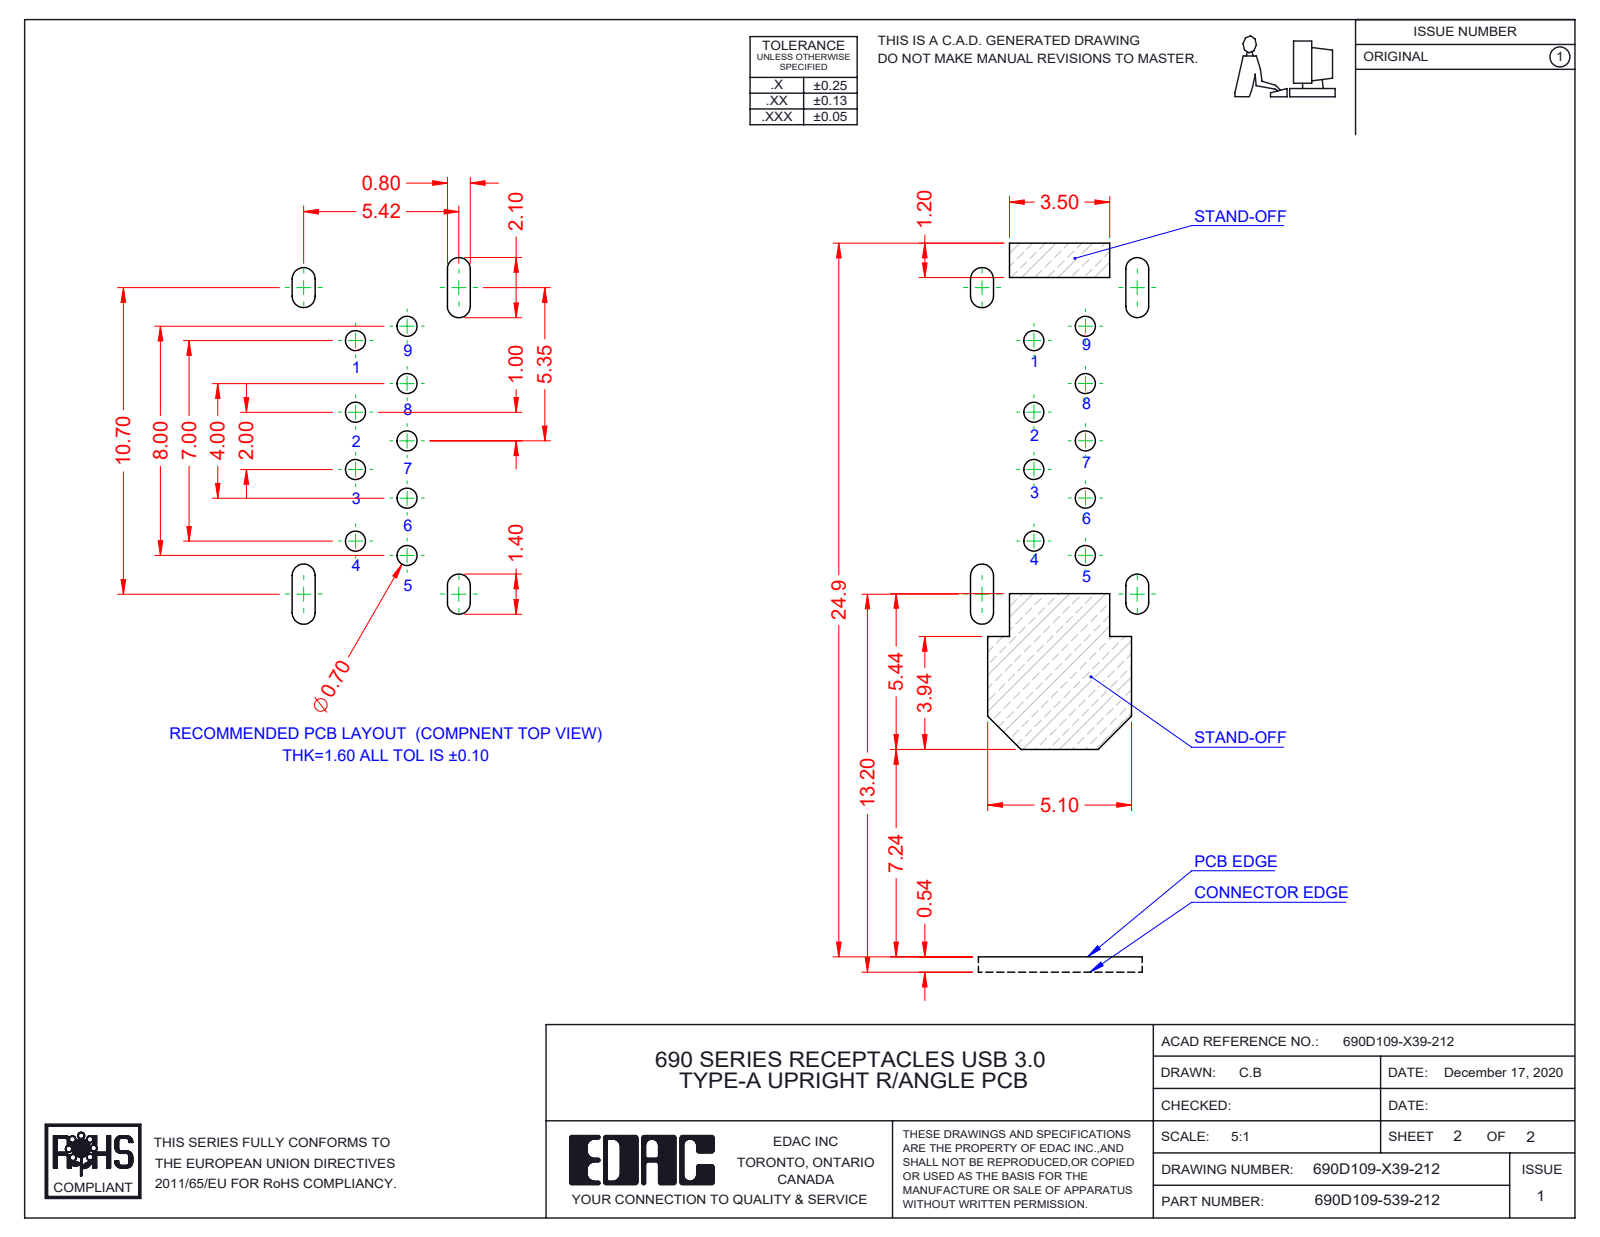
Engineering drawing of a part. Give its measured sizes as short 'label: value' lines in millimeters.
name: Contact 2.0 4 690D109-X39-212; Insulator 2 690D109-X39-212_Blue; Shell 2 690D109-X39-212; Contact 3.0 7 690D109-X39-212 (+8 more)
written by: SolidWorks 2020 (AUTOMOTIVE_DESIGN)
unit: mm
bodies: 13 solids, 2728 faces (1912 planar, 744 cylindrical, 72 other)
size: 25.75 × 16.46 × 6.42
volume: 1 027 mm³; area: 4 307 mm²
holes: 1× ⌀0.8
rounds: 74× R0.3, 66× R0.1, 64× R0.2, 43× R0.15, 36× R0.5, 26× R0.6, 24× R0.4, 18× R0.12
face distances: 5.42, 2.84, 0.8, 2.58, 5.72, 2.54, 2.88, 5.12, 1, 1.8
